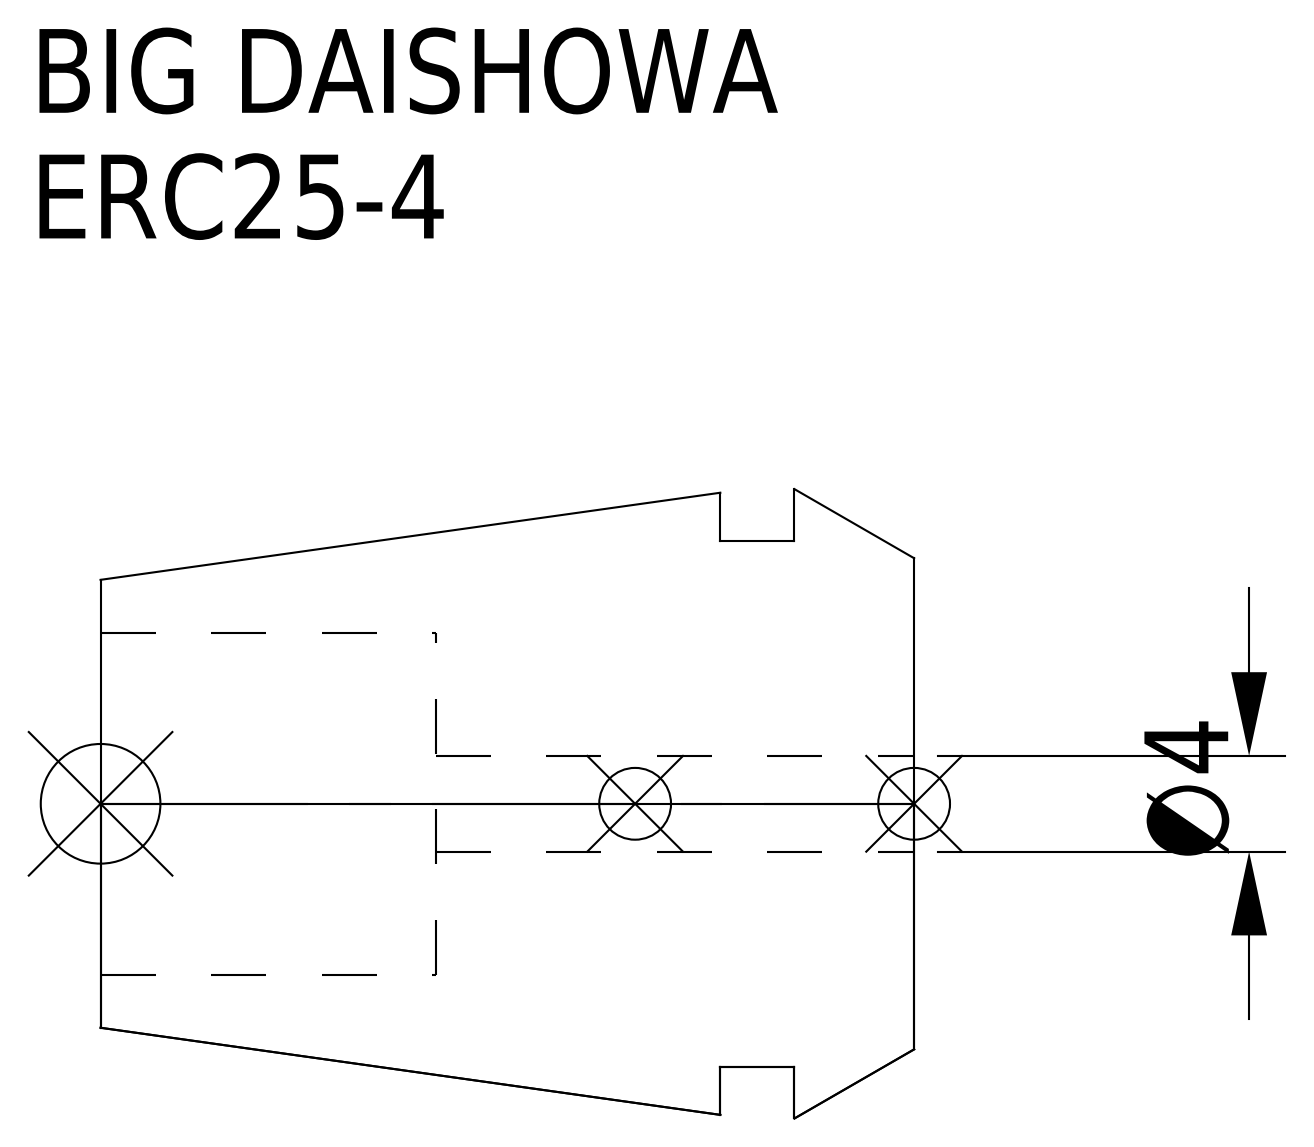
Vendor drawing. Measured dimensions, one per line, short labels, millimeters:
name: ERC25-4
written by: CREO PARAMETRIC BY PTC INC, 2016380 (AUTOMOTIVE_DESIGN)
unit: mm
bodies: 1 solid, 15 faces (5 planar, 6 cylindrical, 4 other)
size: 34 × 26.3 × 26.3
volume: 11 103 mm³; area: 4 251 mm²
holes: 1× ⌀4, 1× ⌀14.3
bosses: 1× ⌀22
face distances: 5, 8.1, 3.1, 20, 15, 11.9, 34, 29, 25.9, 14
